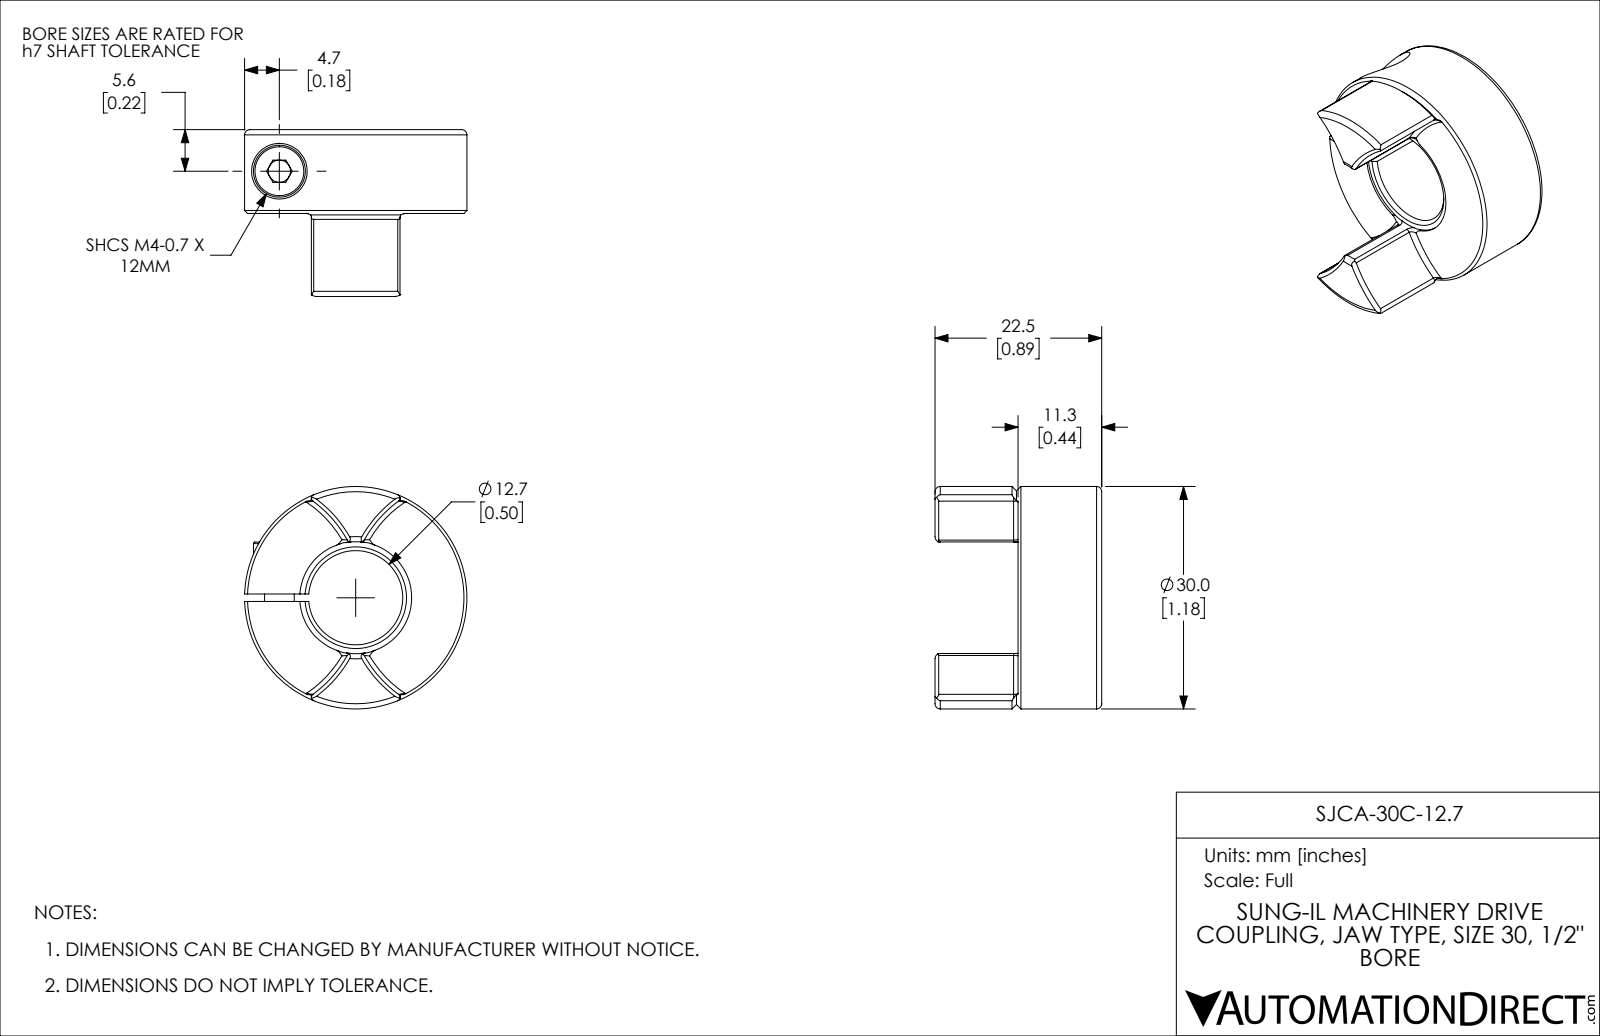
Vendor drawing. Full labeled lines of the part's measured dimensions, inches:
Part name (STEP PRODUCT): SJCA-30C-12.7
STEP written by: SolidWorks 2021 (CONFIG_CONTROL_DESIGN)
Units: inches
Bodies: 2 solids, 109 faces (27 planar, 41 cylindrical, 41 other)
Overall size (bounding box): 1.181 × 1.181 × 0.886
Volume: 0.45 in³ · Surface area: 6.265 in²
Round holes (diameter × count): ⌀0.118 ×1, ⌀0.13 ×1, ⌀0.173 ×1, ⌀0.295 ×1, ⌀0.5 ×1, ⌀0.594 ×1
Round bosses / shafts (diameter × count): ⌀1.181 ×1, ⌀0.276 ×1, ⌀0.157 ×1
Partial cylindrical surfaces — rounded edges, fillets, slot ends (radius × count): R0.02 ×8, R0.634 ×2, R1.083 ×1
Main face-to-face distances: 0.445, 0.039, 0.157, 0.441, 0.886, 0.118, 0.315, 0.453, 0.433, 0.276
